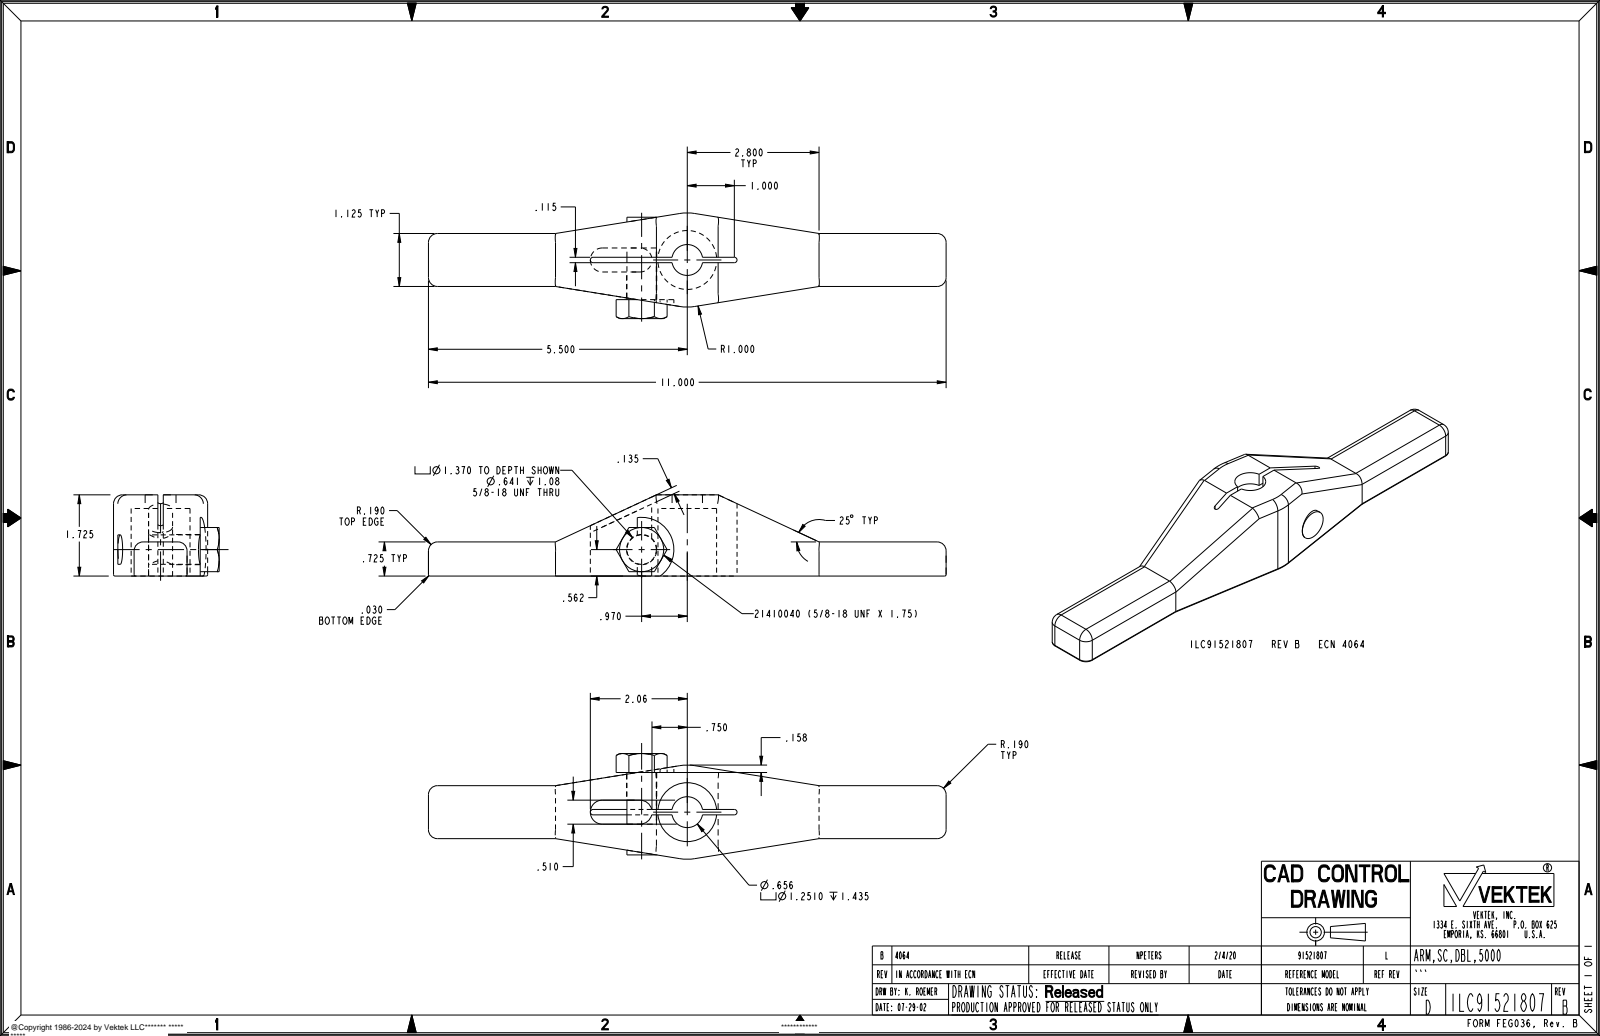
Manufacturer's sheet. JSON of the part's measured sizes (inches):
{"part_name": "ILC91521807", "step_written_by": "PRO/ENGINEER BY PARAMETRIC TECHNOLOGY CORPORATION, 2013320 (AUTOMOTIVE_DESIGN)", "units": "inches", "bodies": {"solids": 1, "faces": 105, "planar": 37, "cylindrical": 50, "other": 18}, "overall_size": [11, 2.245, 1.725], "volume_in3": 14.14, "surface_area_in2": 68.45, "round_holes": [[0.641, 1], [0.656, 1], [1.251, 1]], "round_bosses_or_shafts": [[0.625, 1]], "partial_cylinders_radius": [[0.19, 16], [0.03, 8], [0.057, 2], [0.255, 2], [0.685, 1], [1, 1]], "face_to_face_distances": [0.725, 1.999, 1.125, 0.505, 0.62, 2.001, 0.307, 0.818, 0.198, 0.313]}
